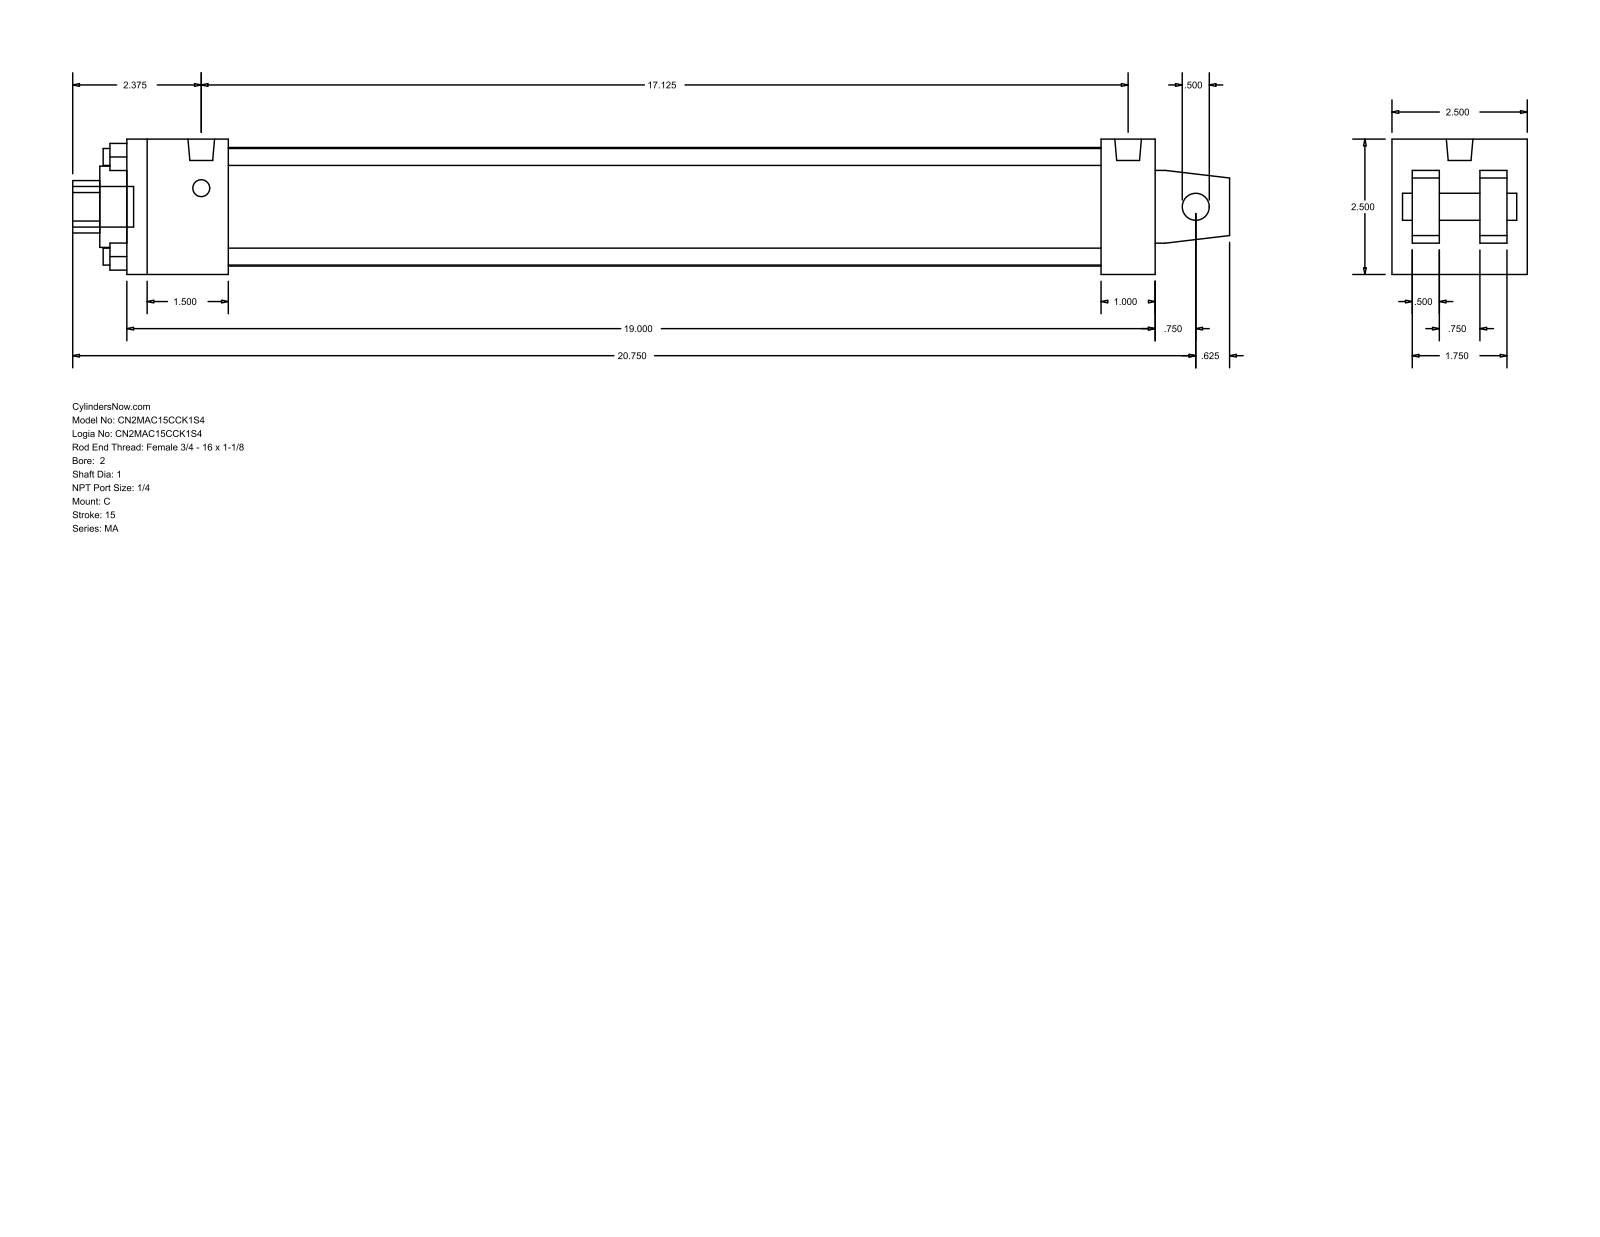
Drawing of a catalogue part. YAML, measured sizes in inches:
part_name: "MA_C__0200_1"
step_written_by: "GSSL Pune (CONFIG_CONTROL_DESIGN)"
units: inches
bodies: {solids: 0, faces: 103, planar: 76, cylindrical: 27, other: 0}
overall_size: [21.375, 2.5, 2.5]
round_holes:
  - {diameter: 0.313, count: 4}
  - {diameter: 0.5, count: 1}
  - {diameter: 1, count: 1}
  - {diameter: 1.5, count: 1}
  - {diameter: 2.19, count: 1}
round_bosses_or_shafts:
  - {diameter: 0.313, count: 4}
  - {diameter: 0.492, count: 2}
  - {diameter: 0.75, count: 1}
partial_cylinders:
  - {radius: 0.484, count: 1}
face_to_face_distances: [2.5, 0.5, 19, 0.875, 1.625, 0.375, 2.125, 1.25, 1.875, 1]
hole_center_spacings: [1.301, 1.84, 2.602]
